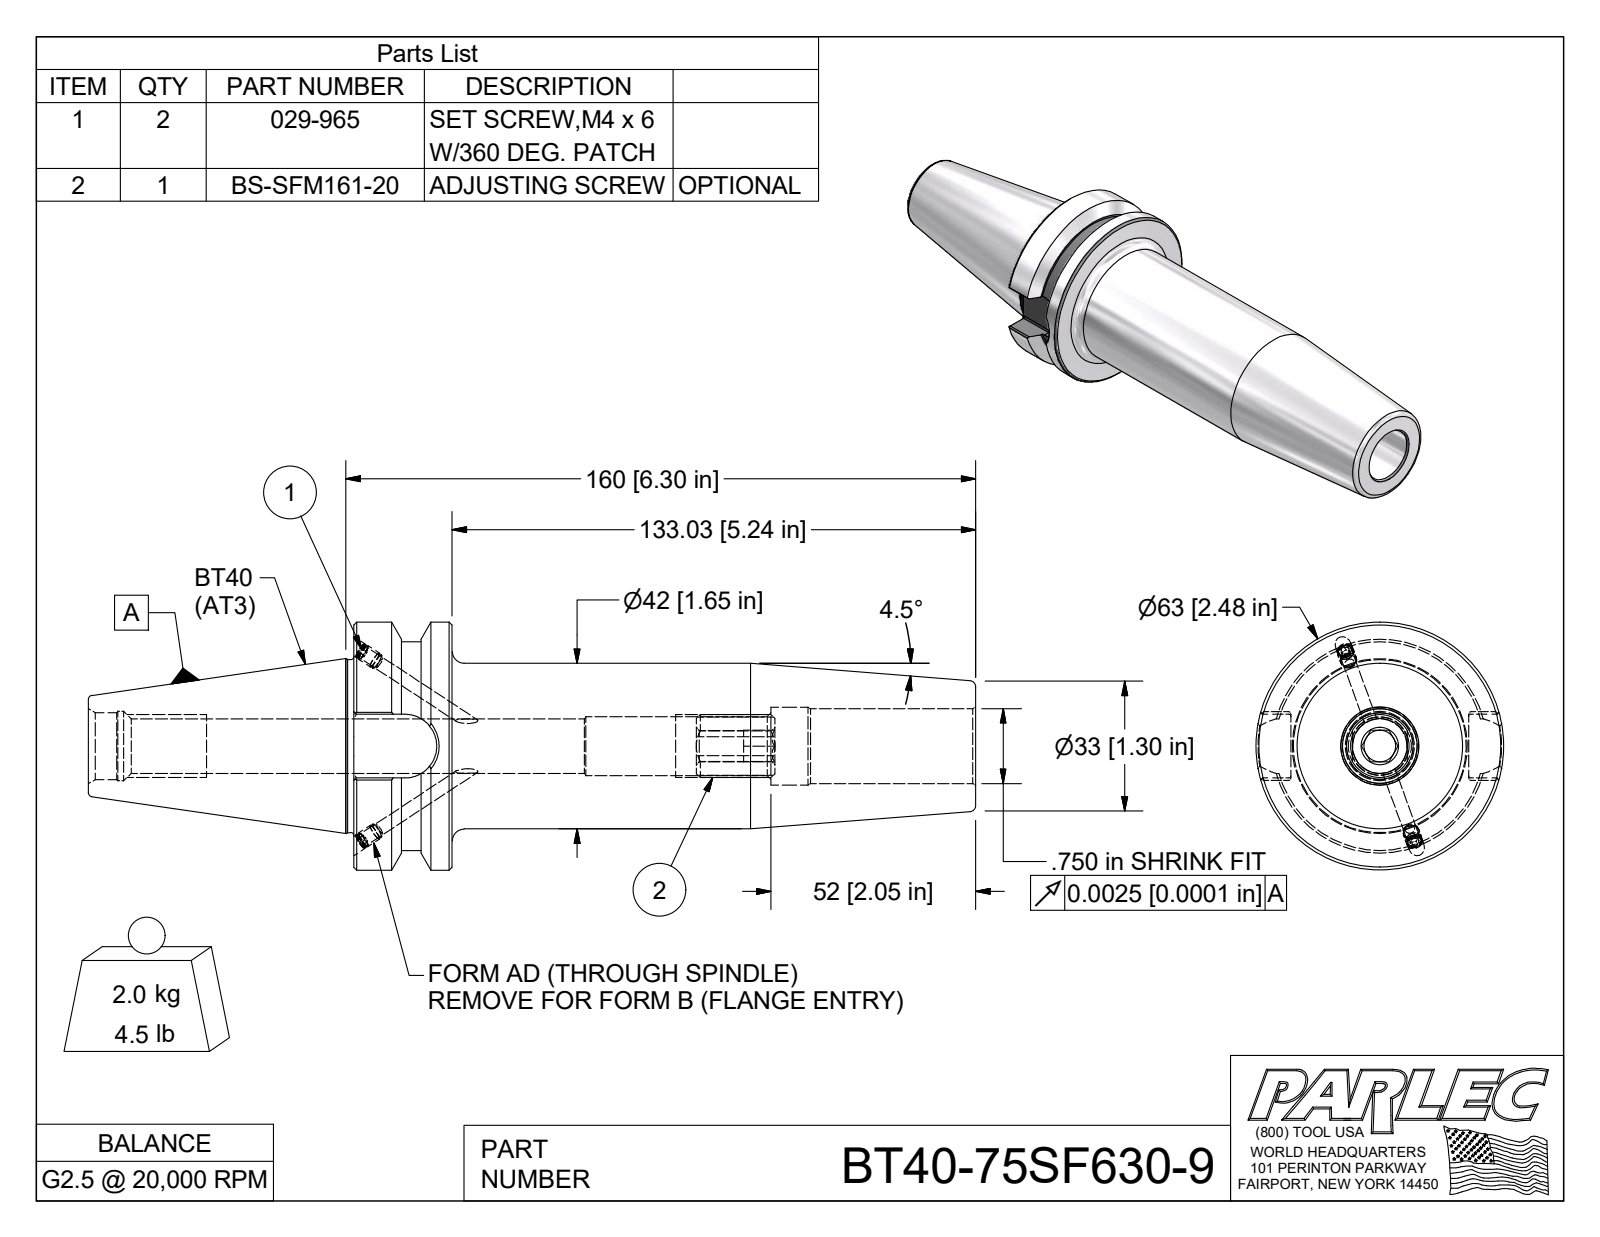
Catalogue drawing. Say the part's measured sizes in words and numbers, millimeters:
The part is named "BT40-75SF630-9; BT40BC-75SF630-9-1; 029-965; BS-SFM161-20". Its 3-D file was written by "Autodesk Inventor 2009 (AUTOMOTIVE_DESIGN)". It is 4 solids with 131 faces: 57 planar, 33 cylindrical and 41 other. Overall it measures 225.4 by 63 by 63 millimeters. Its volume is 262 000 cubic millimeters and its surface area 47 720 square millimeters. Round holes: 2 of diameter 3.3, 2 of diameter 4.1, 1 of diameter 17.6, 1 of diameter 19, 1 of diameter 19.8. Round bosses or shafts: 2 of diameter 4.2, 2 of diameter 4, 1 of diameter 63, 1 of diameter 53, 1 of diameter 44.5, 1 of diameter 43.9, 1 of diameter 42. Partial cylindrical surfaces (rounded edges, fillets, slot ends): 8 of radius 0.5, 1 of radius 8, 1 of radius 8.1. The main face-to-face distances are 25, 158, 133, 15.6, 29.6, 45.2, 67.4, 92.4, 225.4, 14.
